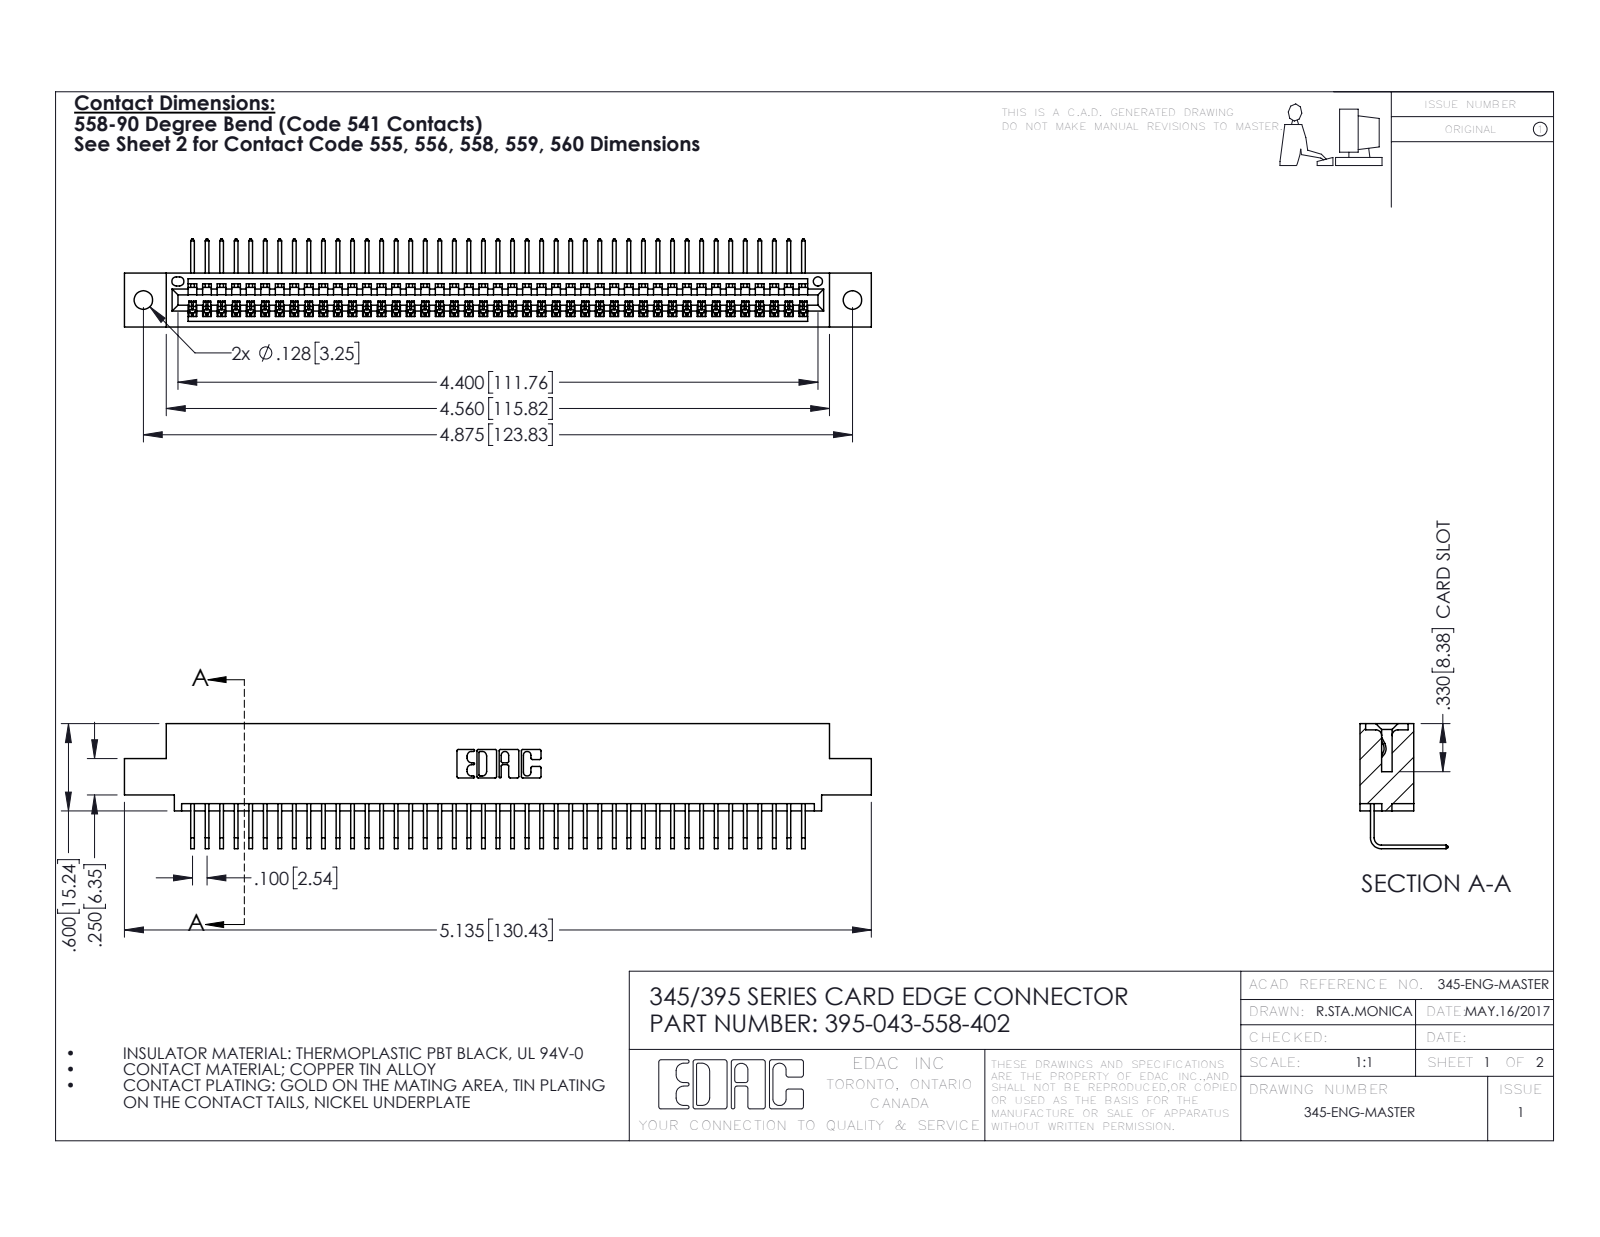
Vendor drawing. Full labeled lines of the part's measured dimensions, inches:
Part name (STEP PRODUCT): 345 Part_0.110 Offset - 0.128 Dia; 395-043-558-402; 345-292-001_558 Tail - 2
STEP written by: SolidWorks 2016 (CONFIG_CONTROL_DESIGN)
Units: inches
Bodies: 44 solids, 2710 faces (1890 planar, 820 cylindrical, 0 other)
Overall size (bounding box): 5.135 × 0.859 × 0.605
Volume: 0.759 in³ · Surface area: 26.63 in²
Round holes (diameter × count): ⌀0.128 ×2, ⌀0.064 ×1
Partial cylindrical surfaces — rounded edges, fillets, slot ends (radius × count): R0.006 ×86, R0.01 ×22, R0.007 ×6, R0.031 ×6, R0.026 ×3, R0.031 ×2, R0.04 ×2, R0.014 ×1
Main face-to-face distances: 0.072, 0.298, 0.37, 0.2, 0.098, 0.272, 0.025, 0.225, 0.149, 0.072
Hole centre spacings: 0.27, 4.639, 4.875
